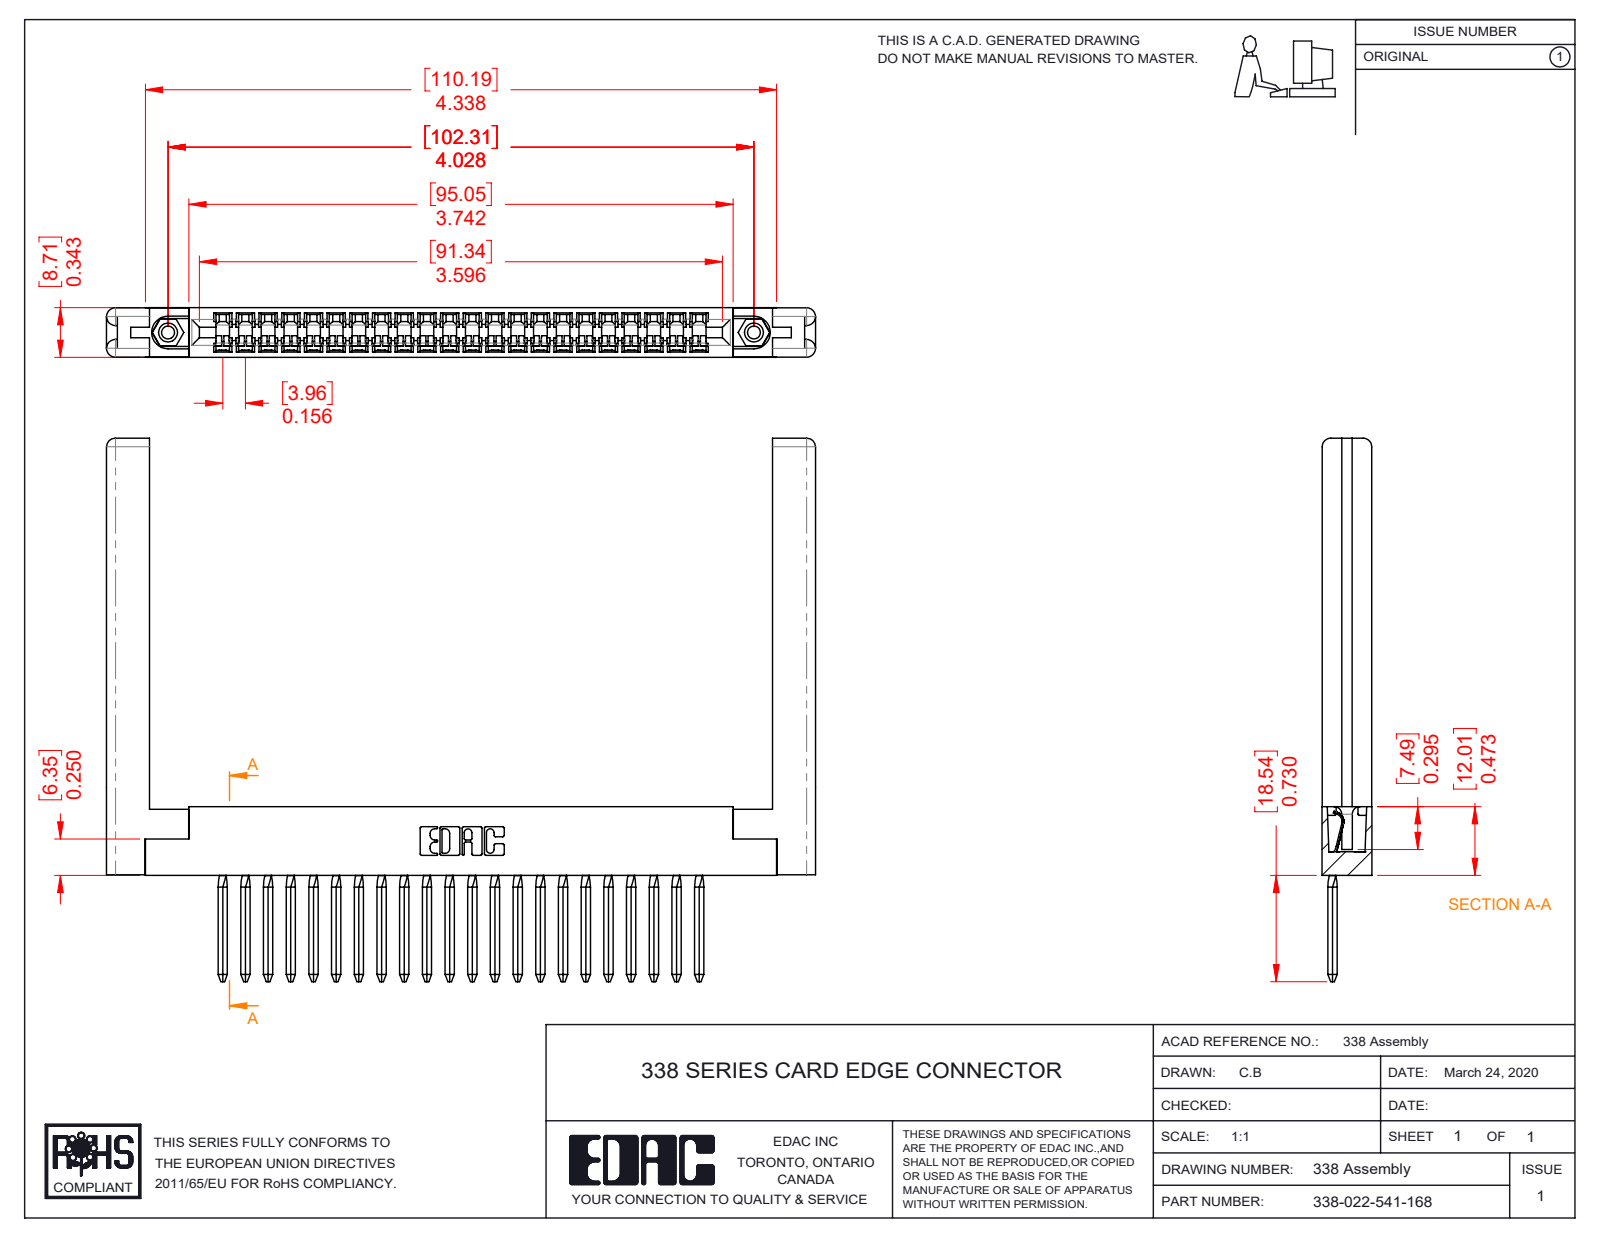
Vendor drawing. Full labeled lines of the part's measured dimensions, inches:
Part name (STEP PRODUCT): 307-220-058; 338-290-001_541; 338-022-541-168; 345-250-001_345-250-001-102 (+1 more)
STEP written by: SolidWorks 2016 (CONFIG_CONTROL_DESIGN)
Units: inches
Bodies: 27 solids, 2282 faces (1564 planar, 606 cylindrical, 112 other)
Overall size (bounding box): 4.874 × 3.735 × 0.343
Volume: 0.994 in³ · Surface area: 29.58 in²
Round holes (diameter × count): ⌀0.089 ×2, ⌀0.125 ×2, ⌀0.156 ×2
Round bosses / shafts (diameter × count): ⌀0.155 ×2
Partial cylindrical surfaces — rounded edges, fillets, slot ends (radius × count): R0.025 ×90, R0.008 ×22, R0.01 ×22, R0.055 ×18, R0.067 ×18, R0.1 ×17, R0.061 ×8, R0.007 ×6
Main face-to-face distances: 0.341, 0.343, 0.34, 0.136, 0.207, 0.134, 0.206, 0.22, 4.284, 0.071
Hole centre spacings: 4.028
